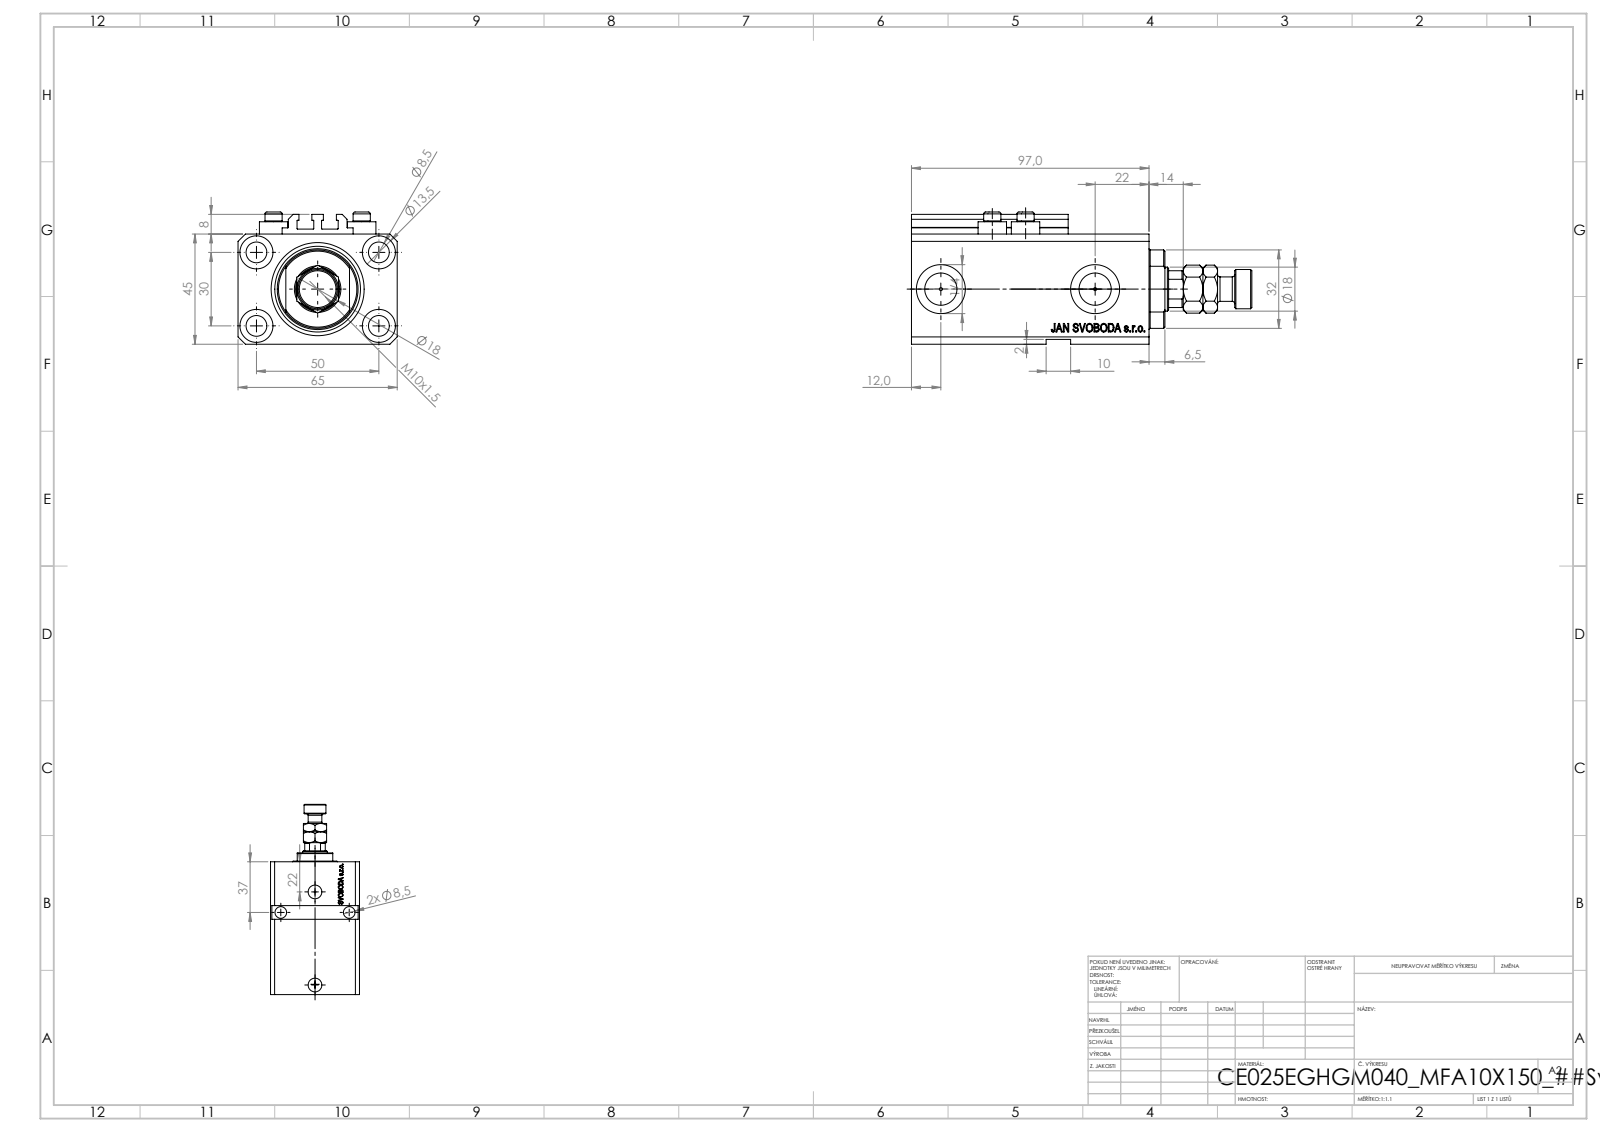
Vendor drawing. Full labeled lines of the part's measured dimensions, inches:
Part name (STEP PRODUCT): ALLEN BOLT V250CE; V250CE_VC_E; MFA; V250CE_C_VCP (+1 more)
STEP written by: SolidWorks 2019 (CONFIG_CONTROL_DESIGN)
Units: inches
Bodies: 9 solids, 1119 faces (527 planar, 130 cylindrical, 462 other)
Overall size (bounding box): 5.472 × 2.559 × 2.126
Volume: 15.66 in³ · Surface area: 112.2 in²
Round holes (diameter × count): ⌀0.335 ×7, ⌀0.049 ×4, ⌀0.157 ×4, ⌀0.531 ×4, ⌀0.394 ×2, ⌀0.518 ×2, ⌀0.787 ×2, ⌀0.709 ×1, ⌀0.984 ×1, ⌀1.496 ×1
Round bosses / shafts (diameter × count): ⌀0.457 ×4, ⌀0.276 ×4, ⌀0.63 ×1, ⌀0.394 ×1
Partial cylindrical surfaces — rounded edges, fillets, slot ends (radius × count): R0.008 ×10, R0.335 ×1, R0.63 ×1
Main face-to-face distances: 1.772, 2.559, 0.551, 3.268, 0.079, 3.819, 1.85, 0.272, 0.807, 2.996
Hole centre spacings: 1.148, 1.969, 0.535, 0.595, 1.098, 1.181, 1.228, 1.245
